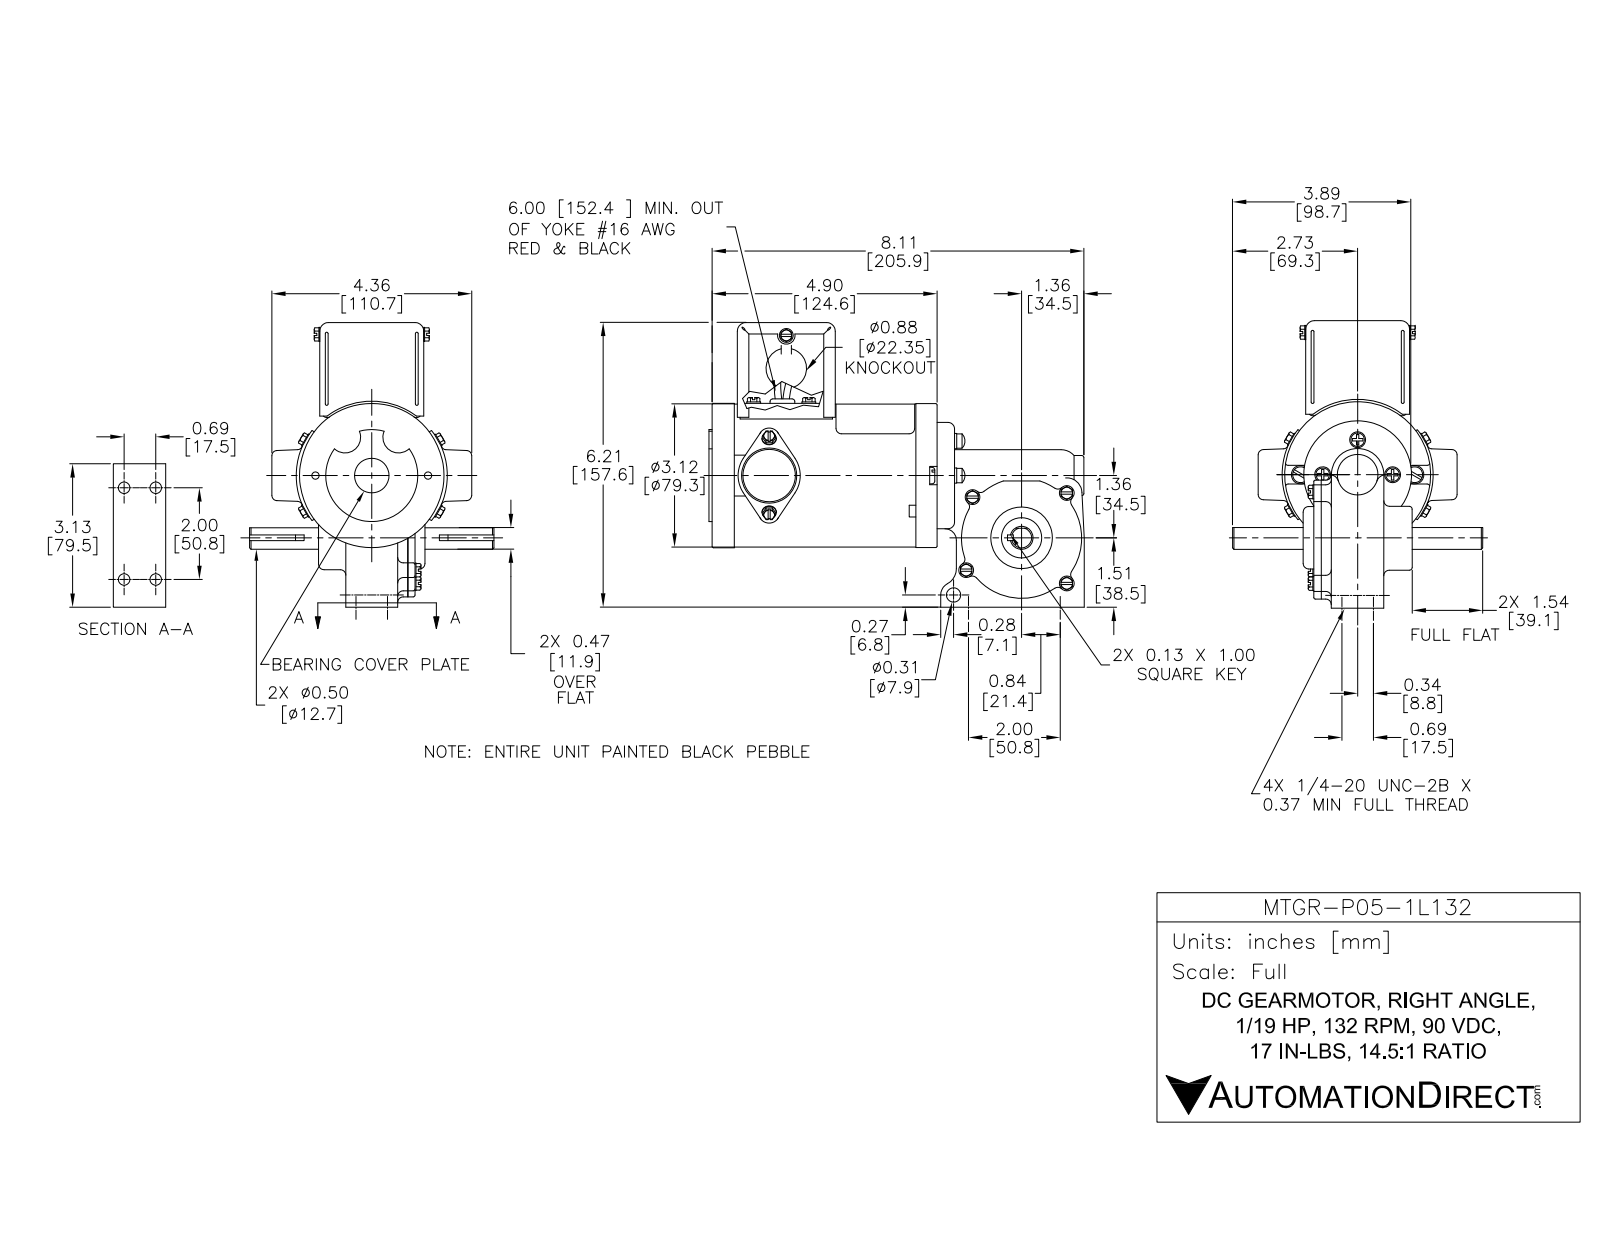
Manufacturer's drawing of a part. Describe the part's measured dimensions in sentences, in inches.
The part is named "P05-1L132". Its 3-D file was written by "SolidWorks 2013 (AUTOMOTIVE_DESIGN)". It is 40 solids with 712 faces: 436 planar, 210 cylindrical and 66 other. Overall it measures 8.179 by 6.274 by 5.453 inches. Its volume is 27.37 cubic inches and its surface area 297.1 square inches. Round holes: 5 of diameter 0.25, 2 of diameter 0.094, 2 of diameter 0.198, 1 of diameter 0.3, 1 of diameter 0.301, 1 of diameter 0.375, 1 of diameter 0.5, 1 of diameter 0.86, 1 of diameter 1.225, 1 of diameter 3, 1 of diameter 3.125. Round bosses or shafts: 4 of diameter 0.321, 4 of diameter 0.3, 3 of diameter 0.346, 3 of diameter 0.295, 2 of diameter 0.125, 2 of diameter 0.1, 1 of diameter 3.156, 1 of diameter 3.14. Partial cylindrical surfaces (rounded edges, fillets, slot ends): 10 of radius 0.1, 4 of radius 0.191, 4 of radius 0.234, 2 of radius 0.15, 2 of radius 0.159, 2 of radius 0.341, 1 of radius 0.25, 1 of radius 0.34. The main face-to-face distances are 0.031, 0.25, 0.063, 4.65, 2.135, 0.307, 2.047, 1.67, 1.608, 0.245. The hole center spacings are 0.343, 0.456, 0.686, 1.23, 2, 2.029, 2.114, 2.326.
